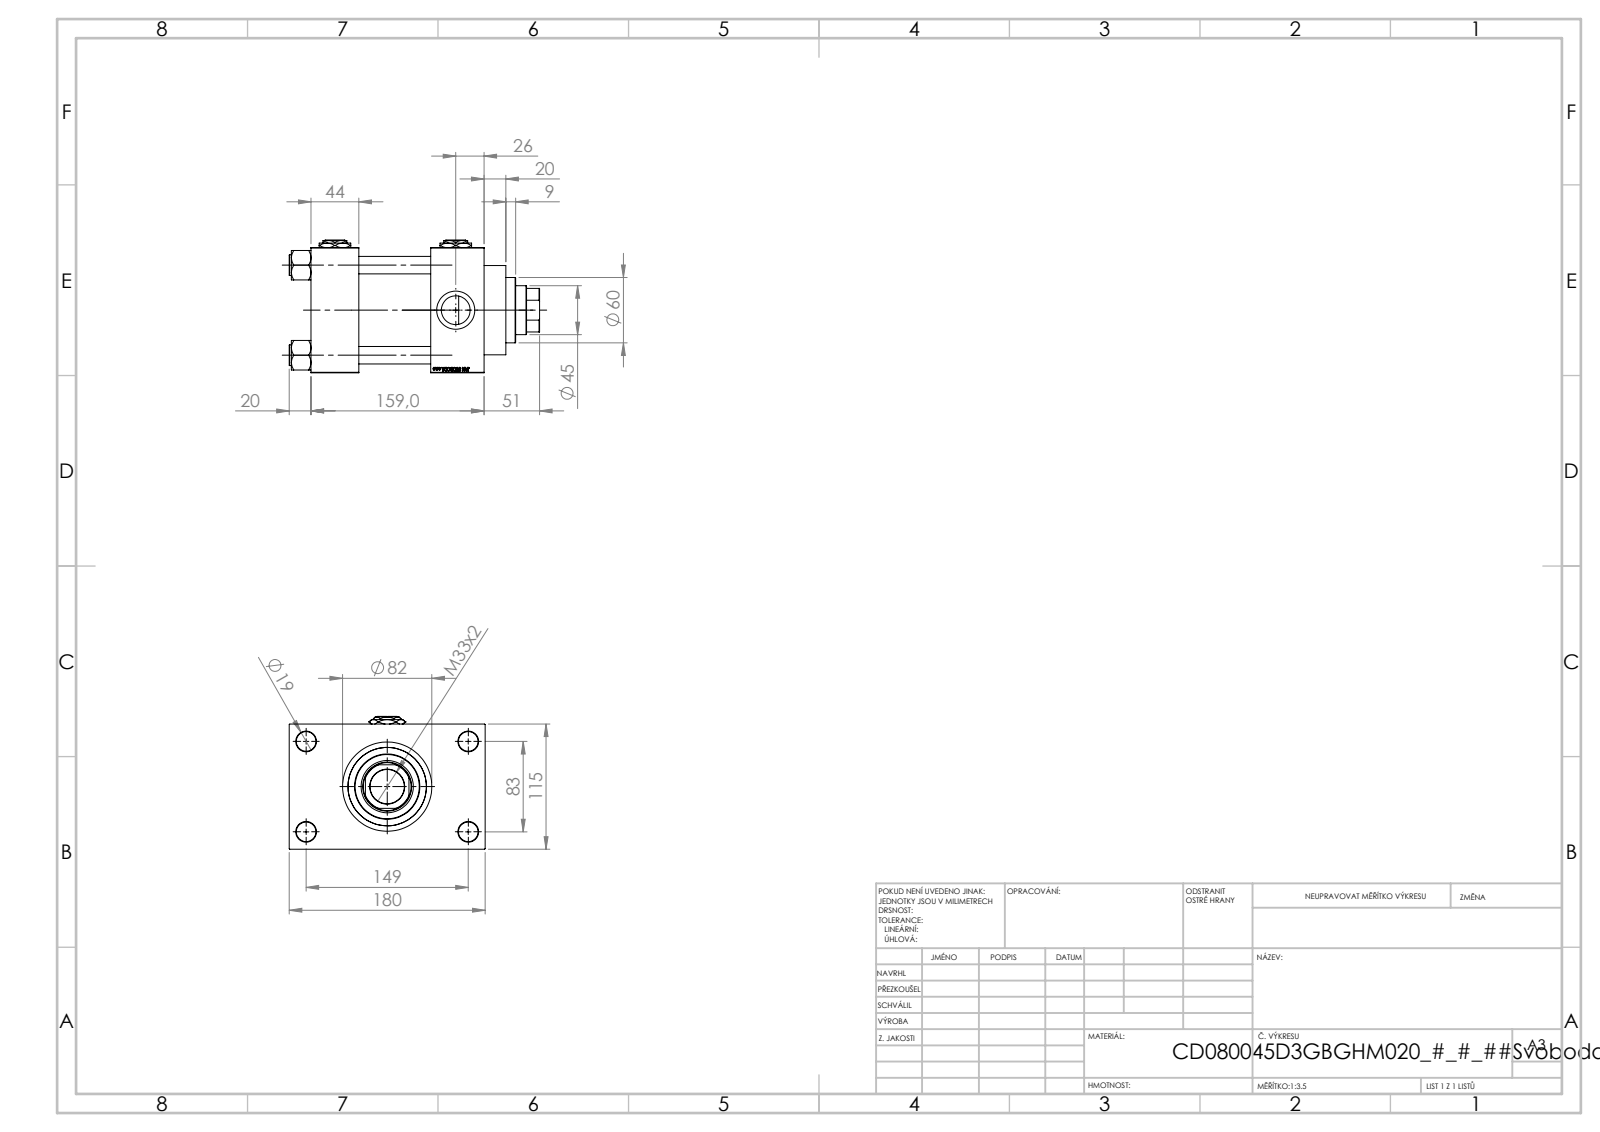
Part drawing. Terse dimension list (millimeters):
name: V215CD_VCP_D; V215CD_NUT_M5_D; V215CD_D_Body; V215CD_D_TYCINKA (+2 more)
written by: SolidWorks 2019 (CONFIG_CONTROL_DESIGN)
unit: mm
bodies: 13 solids, 1252 faces (593 planar, 99 cylindrical, 560 other)
size: 230 × 180 × 122
volume: 1 991 000 mm³; area: 309 018 mm²
holes: 4× ⌀16, 4× ⌀18, 4× ⌀26.44, 4× ⌀35, 3× ⌀7, 1× ⌀31.5, 1× ⌀45, 1× ⌀48, 1× ⌀61, 1× ⌀72, 1× ⌀80
bosses: 4× ⌀19, 1× ⌀86, 1× ⌀82, 1× ⌀60
rounds: 1× R22
face distances: 115, 110, 66, 49, 44, 159, 147.5, 32.5, 20, 69
hole spacings: 33.15, 58.48, 82.7, 85.28, 89.24, 115.85, 142.43, 83
